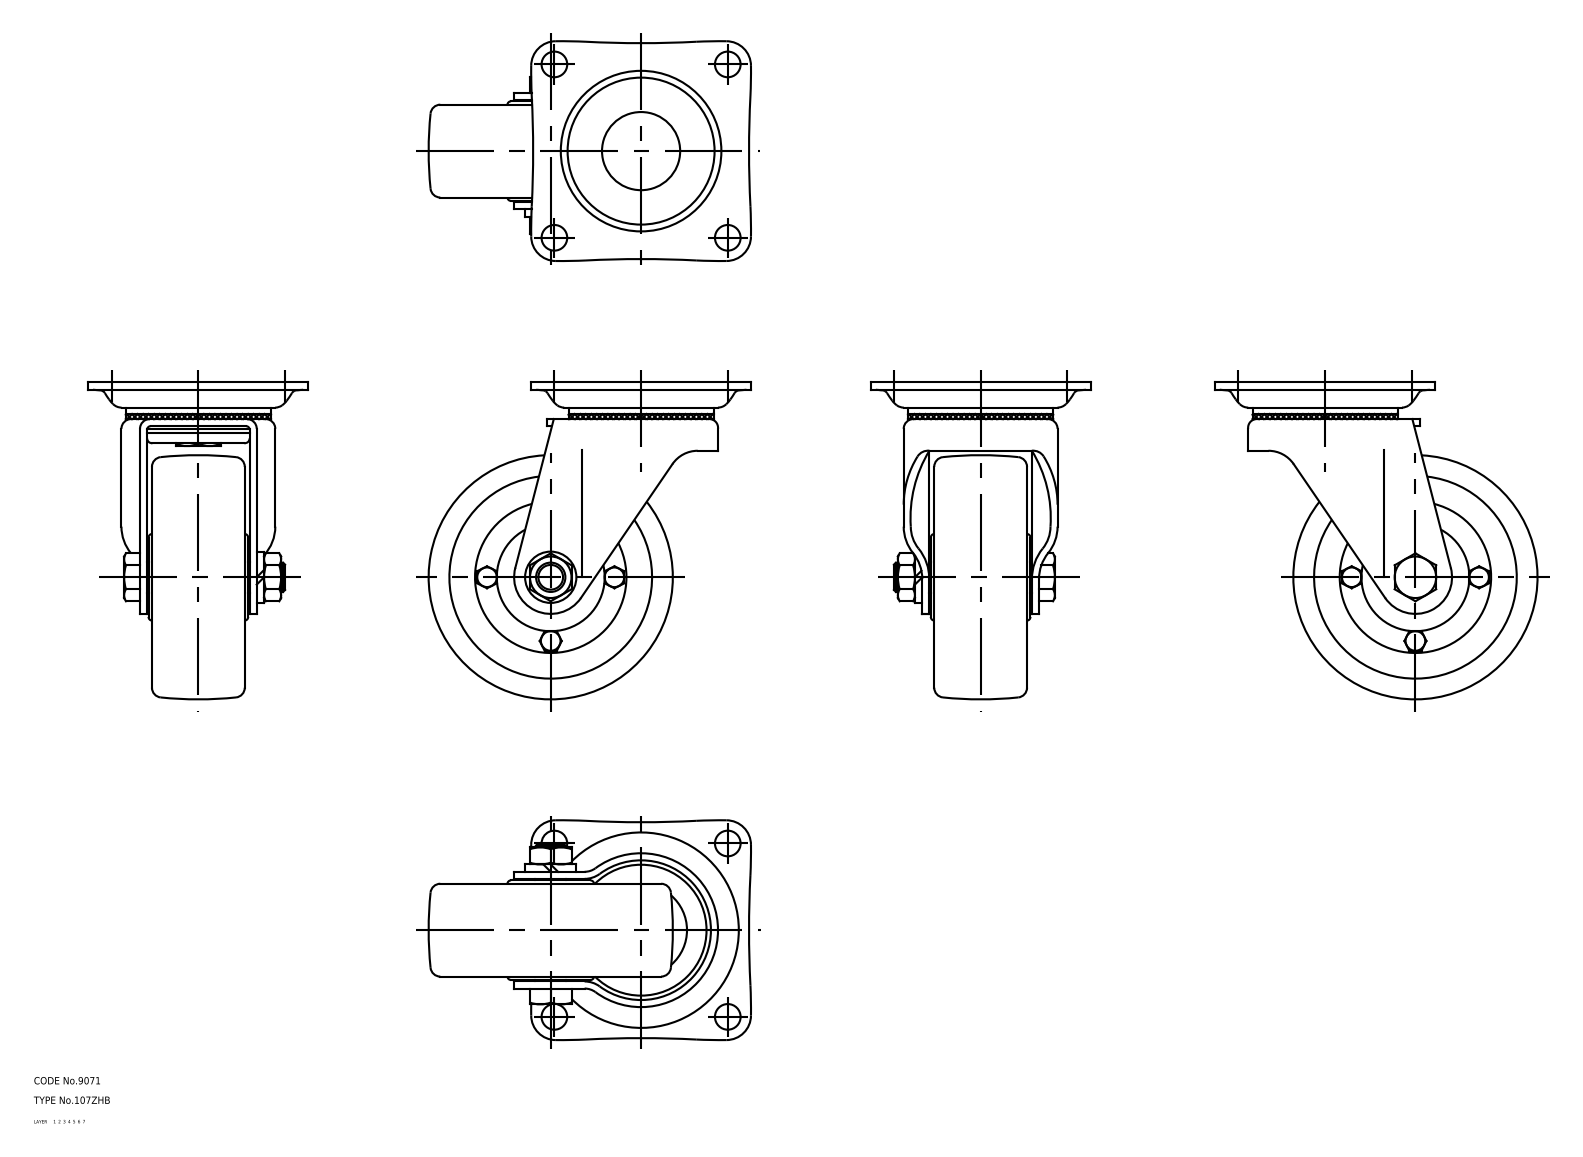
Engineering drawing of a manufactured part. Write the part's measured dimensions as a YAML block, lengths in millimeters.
part_name: "67129092; 67129105; 67129118; 67129131 (+1 more)"
step_written_by: "CADfix (AUTOMOTIVE_DESIGN)"
units: millimeters
bodies: {solids: 5, faces: 348, planar: 0, cylindrical: 0, other: 348}
overall_size: [132.01, 130, 90.02]
volume: 356120
surface_area: 81520
